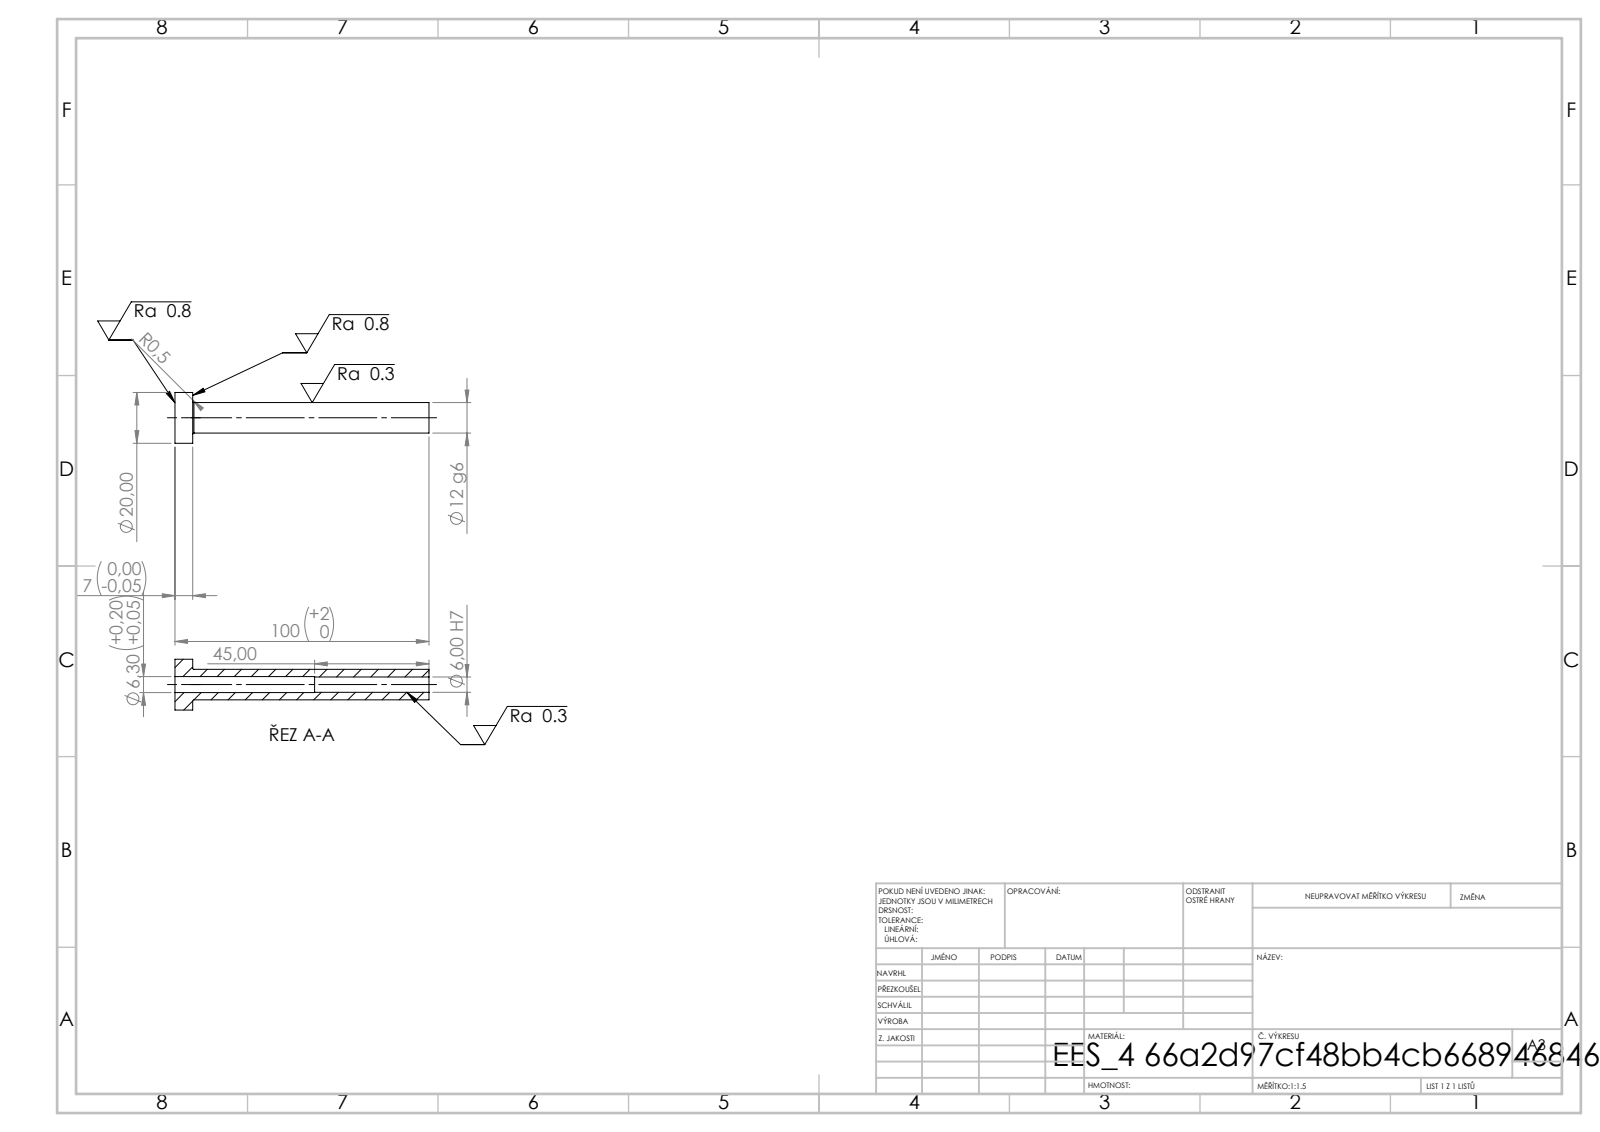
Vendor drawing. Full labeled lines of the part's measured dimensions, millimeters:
STEP written by: SolidWorks 2019 (CONFIG_CONTROL_DESIGN)
Units: millimetres
Bodies: 1 solid, 14 faces (4 planar, 8 cylindrical, 2 other)
Overall size (bounding box): 100 × 20 × 20
Volume: 9 732 mm³ · Surface area: 6 446 mm²
Round holes (diameter × count): ⌀6 ×1, ⌀6.3 ×1
Round bosses / shafts (diameter × count): ⌀20 ×1, ⌀12 ×1
Main face-to-face distances: 7, 100, 93, 55, 48, 45
